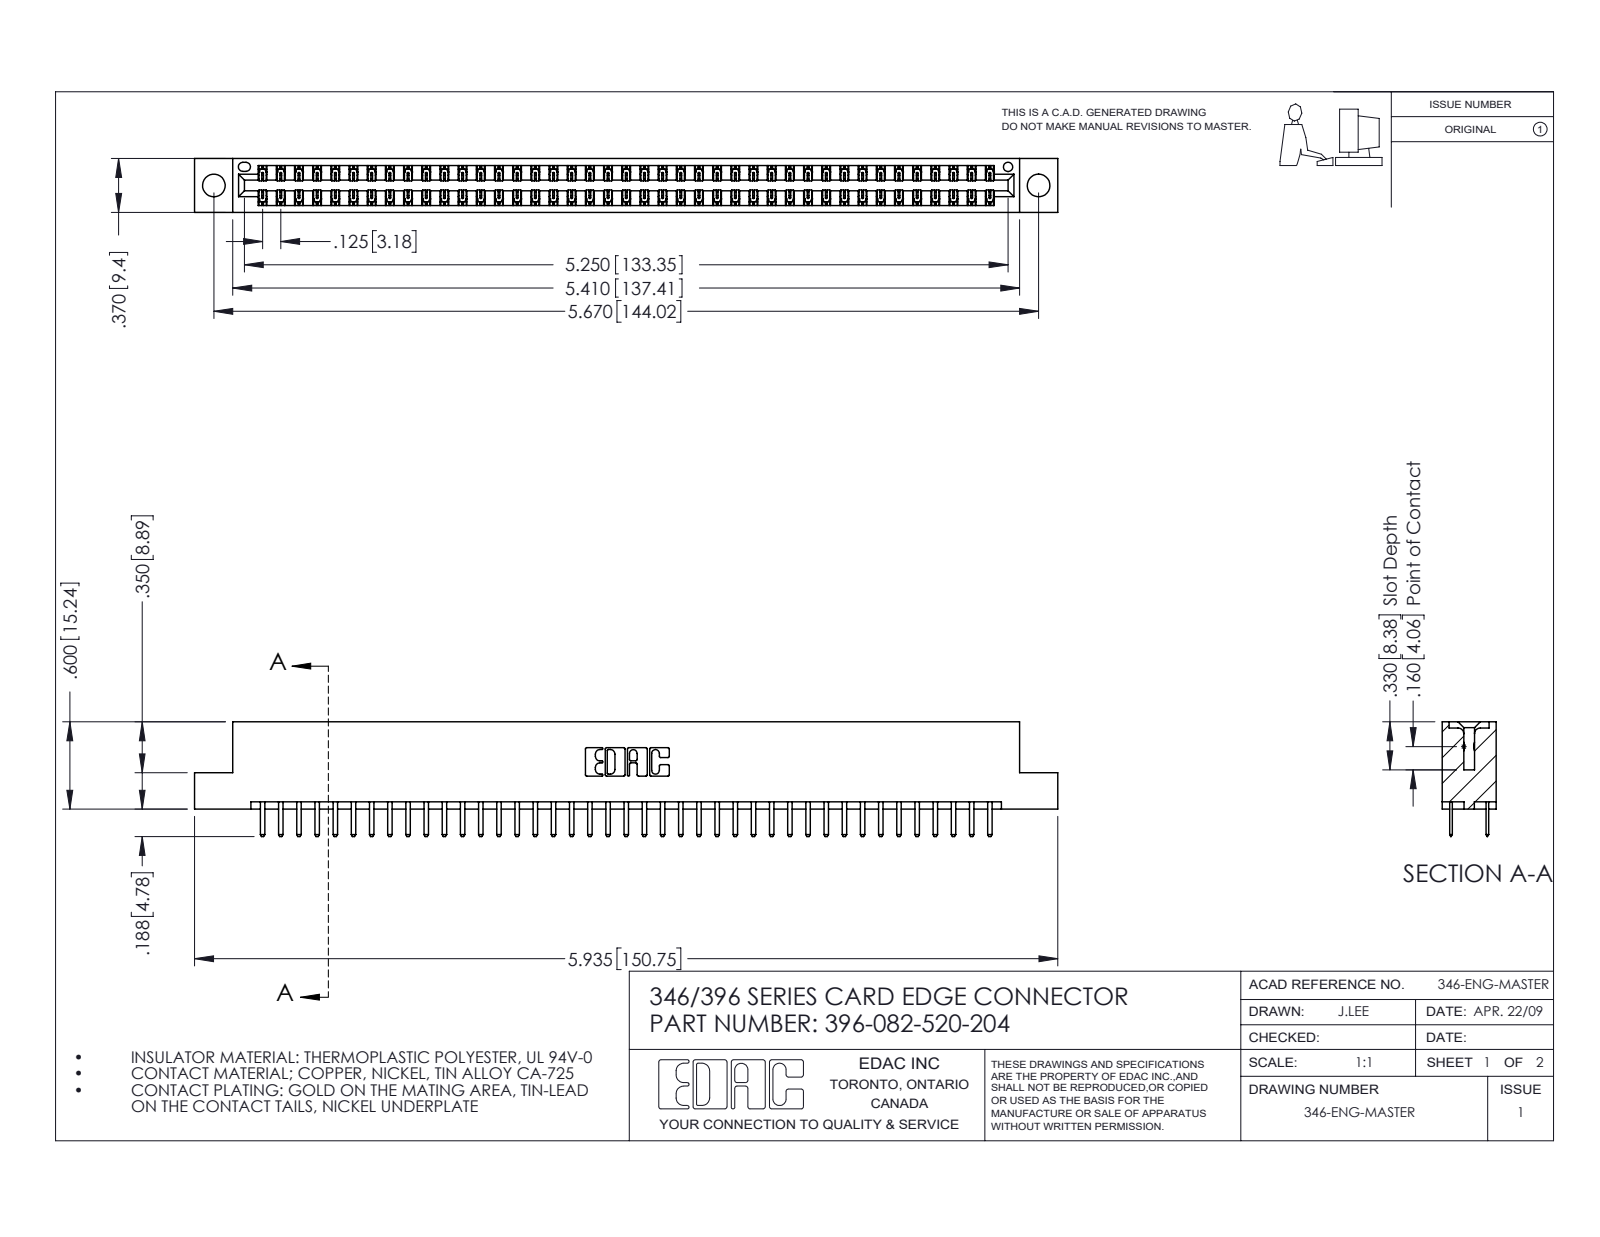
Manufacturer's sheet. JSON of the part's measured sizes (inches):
{"part_name": "396-082-520-204; 346 Part_Flush Mounting Lugs - 0.156 Dia-TH; 345-292-001_345-293-120", "step_written_by": "SolidWorks 2016 (CONFIG_CONTROL_DESIGN)", "units": "inches", "bodies": {"solids": 83, "faces": 4714, "planar": 3110, "cylindrical": 1604, "other": 0}, "overall_size": [5.935, 0.788, 0.37], "volume_in3": 0.889, "surface_area_in2": 30.59, "round_holes": [[0.156, 2], [0.064, 1]], "partial_cylinders_radius": [[0.006, 123], [0.01, 86], [0.01, 22], [0.007, 6], [0.031, 6], [0.026, 3], [0.014, 2], [0.022, 2]], "face_to_face_distances": [0.048, 0.322, 0.25, 0.37, 0.275, 0.072, 0.298, 0.025, 0.148, 0.222], "hole_center_spacings": [0.246, 5.461, 5.67]}
